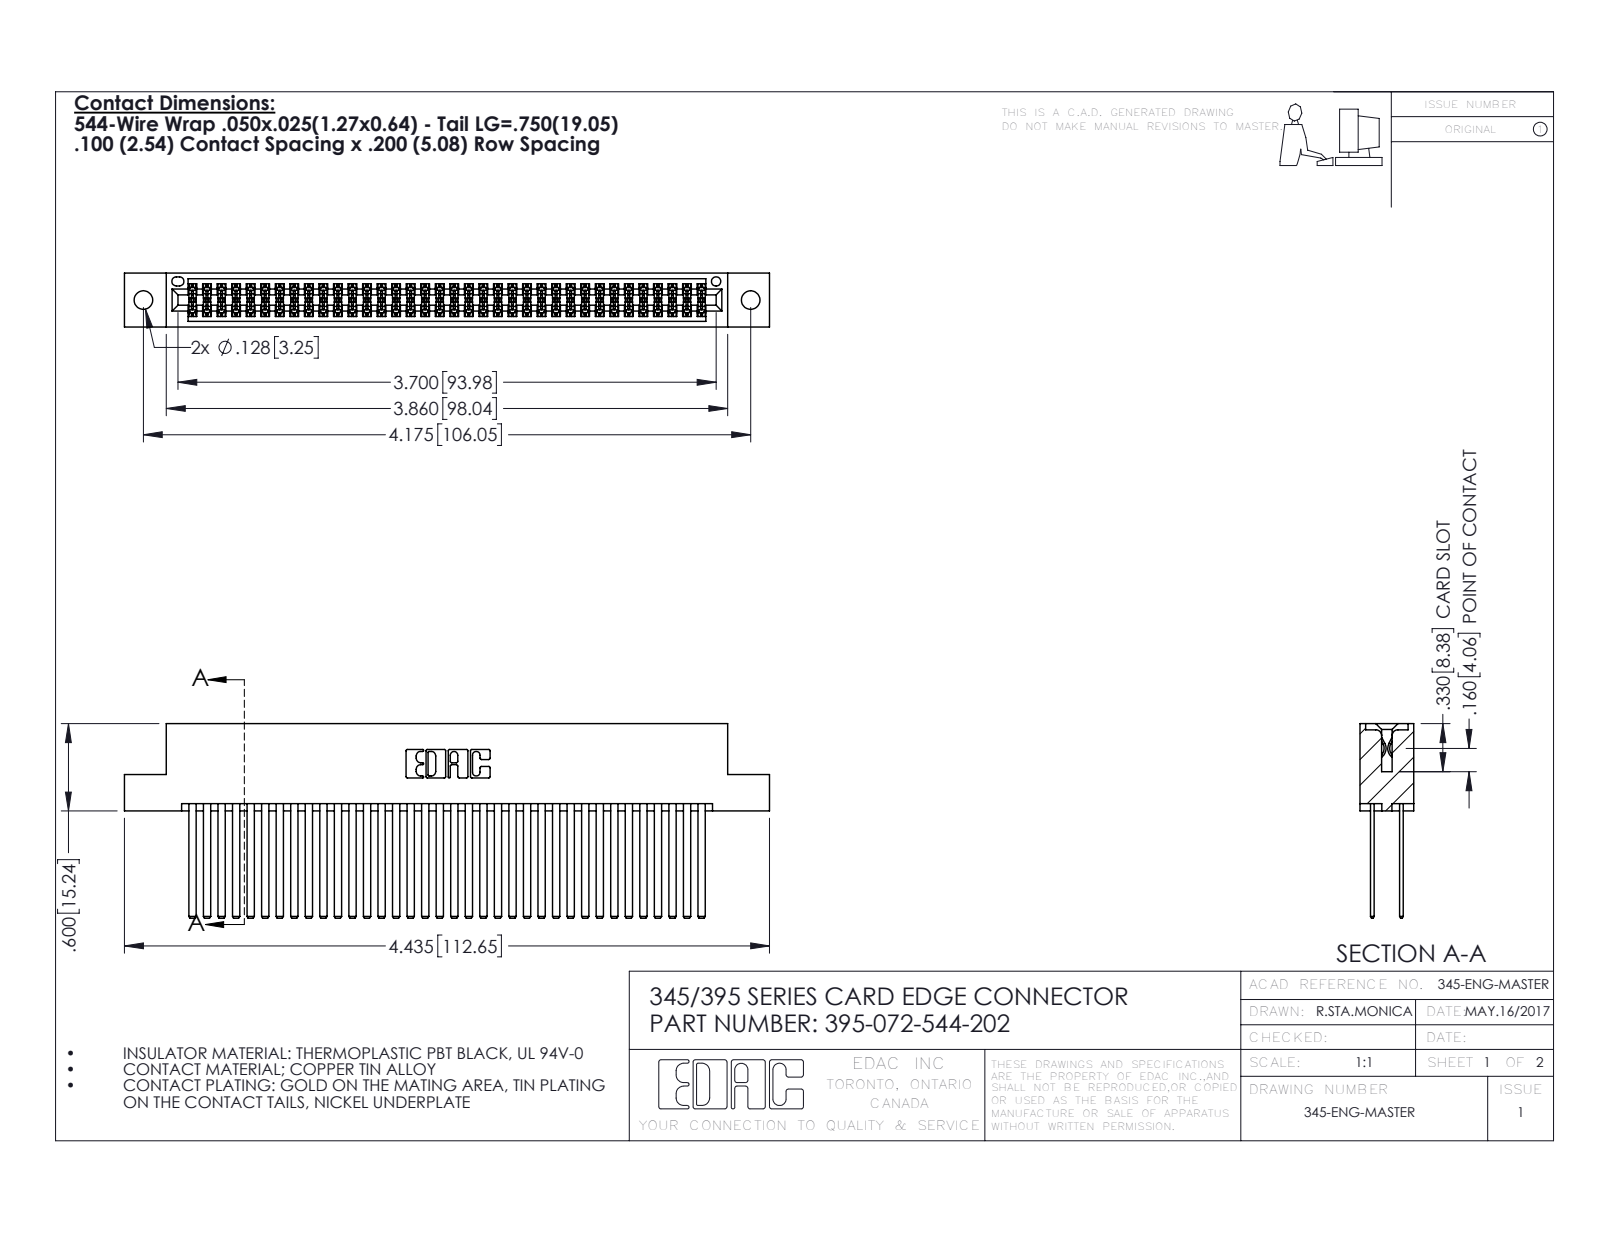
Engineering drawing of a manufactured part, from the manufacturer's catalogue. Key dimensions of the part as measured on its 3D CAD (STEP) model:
Part name (STEP PRODUCT): 395-072-544-202; 345-292-001_345-293-144; 345 Part_Flush Mounting Lugs - 0.128 Dia
STEP written by: SolidWorks 2016 (CONFIG_CONTROL_DESIGN)
Units: inches
Bodies: 73 solids, 3294 faces (2168 planar, 1126 cylindrical, 0 other)
Overall size (bounding box): 4.435 × 1.337 × 0.37
Volume: 0.724 in³ · Surface area: 31.16 in²
Round holes (diameter × count): ⌀0.128 ×2, ⌀0.064 ×1
Partial cylindrical surfaces — rounded edges, fillets, slot ends (radius × count): R0.006 ×108, R0.01 ×22, R0.007 ×6, R0.031 ×6, R0.026 ×3, R0.014 ×2, R0.019 ×2, R0.022 ×2
Main face-to-face distances: 0.2, 0.025, 0.298, 0.072, 0.098, 0.272, 0.225, 0.175, 0.37, 0.05
Hole centre spacings: 0.27, 3.939, 4.175
